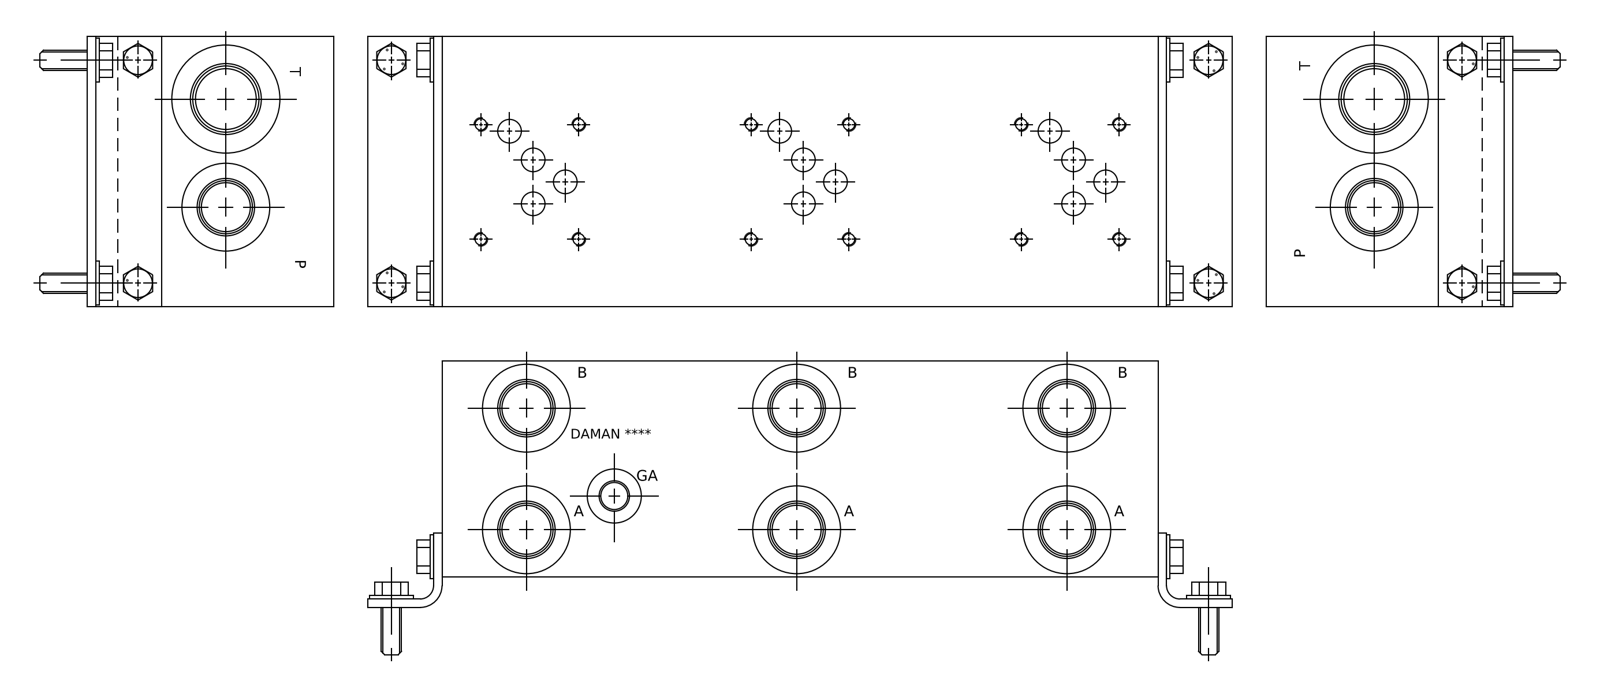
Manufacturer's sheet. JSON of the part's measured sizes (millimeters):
{"part_name": "Part_AD05HP035S_3D", "step_written_by": "Autodesk Inventor 2020 (AUTOMOTIVE_DESIGN)", "units": "millimeters", "bodies": {"solids": 1, "faces": 752, "planar": 400, "cylindrical": 99, "other": 253}, "overall_size": [336.55, 127, 101.6], "volume_mm3": 4118000, "surface_area_mm2": 217048, "round_holes": [[5.11, 12], [6.35, 12], [11.13, 10], [23.01, 7], [24.92, 7], [26.99, 7], [27.43, 7], [42.04, 7], [7.92, 2], [9.53, 2], [11.11, 2], [12.29, 1]], "face_to_face_distances": [101.6, 127, 336.55, 0.79, 126.21, 335.76, 334.97, 19.05, 19.84, 107.16], "hole_center_spacings": [127, 254, 138, 46.05, 70.95, 53.98, 18.27, 29.74]}
